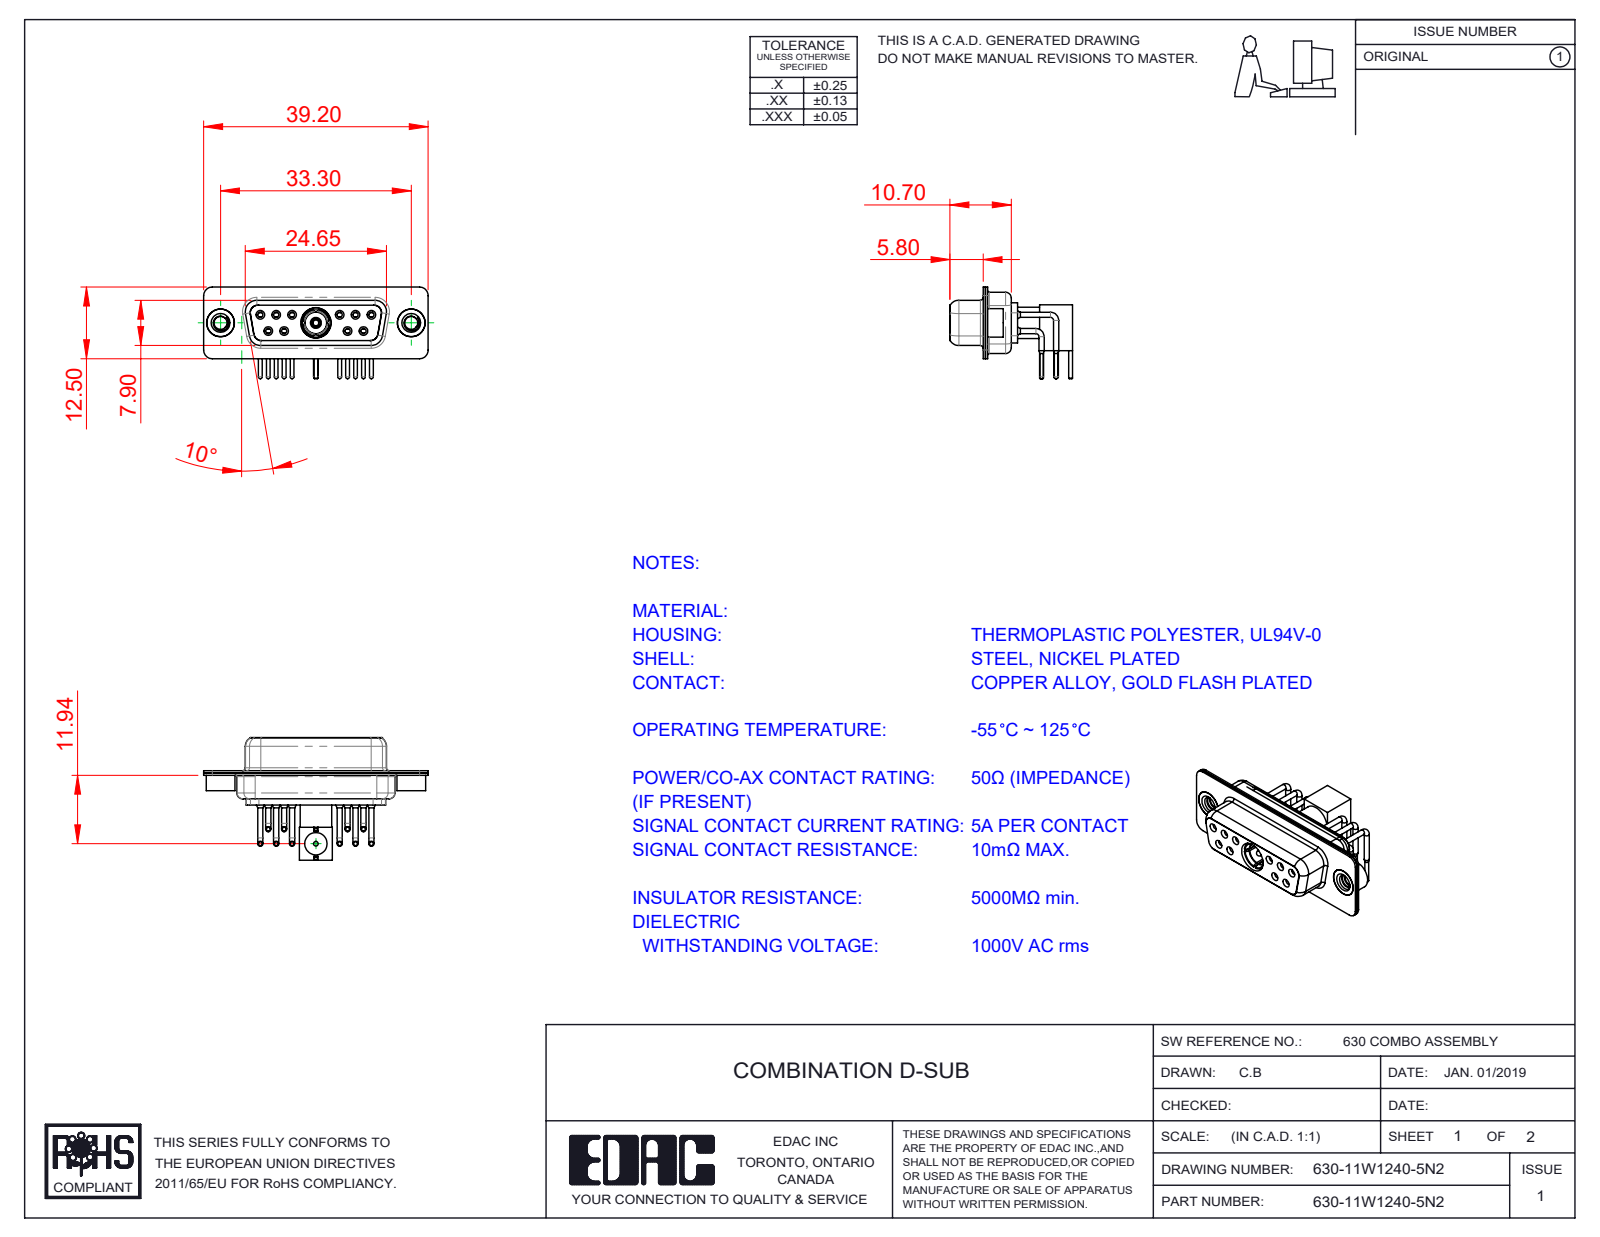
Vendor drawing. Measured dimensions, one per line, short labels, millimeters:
name: Co-Ax Plug_RA PC Tail; Co-Ax Plug Assy_RA; Locking Collar; 630Combo Threaded Rivet_2 (+8 more)
written by: SolidWorks 2020 (CONFIG_CONTROL_DESIGN)
unit: mm
bodies: 21 solids, 977 faces (284 planar, 432 cylindrical, 261 other)
size: 39.2 × 21.41 × 16
volume: 2 813 mm³; area: 6 894 mm²
holes: 11× ⌀1.1, 11× ⌀1.5, 10× ⌀0.9, 10× ⌀2, 6× ⌀1.7, 4× ⌀1.6, 3× ⌀4.85, 2× ⌀2.26, 2× ⌀4, 2× ⌀4.05, 1× ⌀0.8, 1× ⌀2.83
bosses: 10× ⌀0.9, 10× ⌀0.65, 6× ⌀1.6, 3× ⌀5, 2× ⌀4.95, 2× ⌀4.8, 1× ⌀5.5, 1× ⌀5.2
rounds: 16× R1.5, 12× R1.35, 12× R2, 8× R1.6, 4× R0.25, 4× R0.5, 4× R0.6, 4× R0.65
face distances: 0.4, 1.4, 0.45, 1.8, 8.45, 0.8, 8.9, 6.2, 7.05, 1.85
hole spacings: 3.16, 2.77, 13.85, 11.08, 16.62, 5.03, 5.04, 5.54
